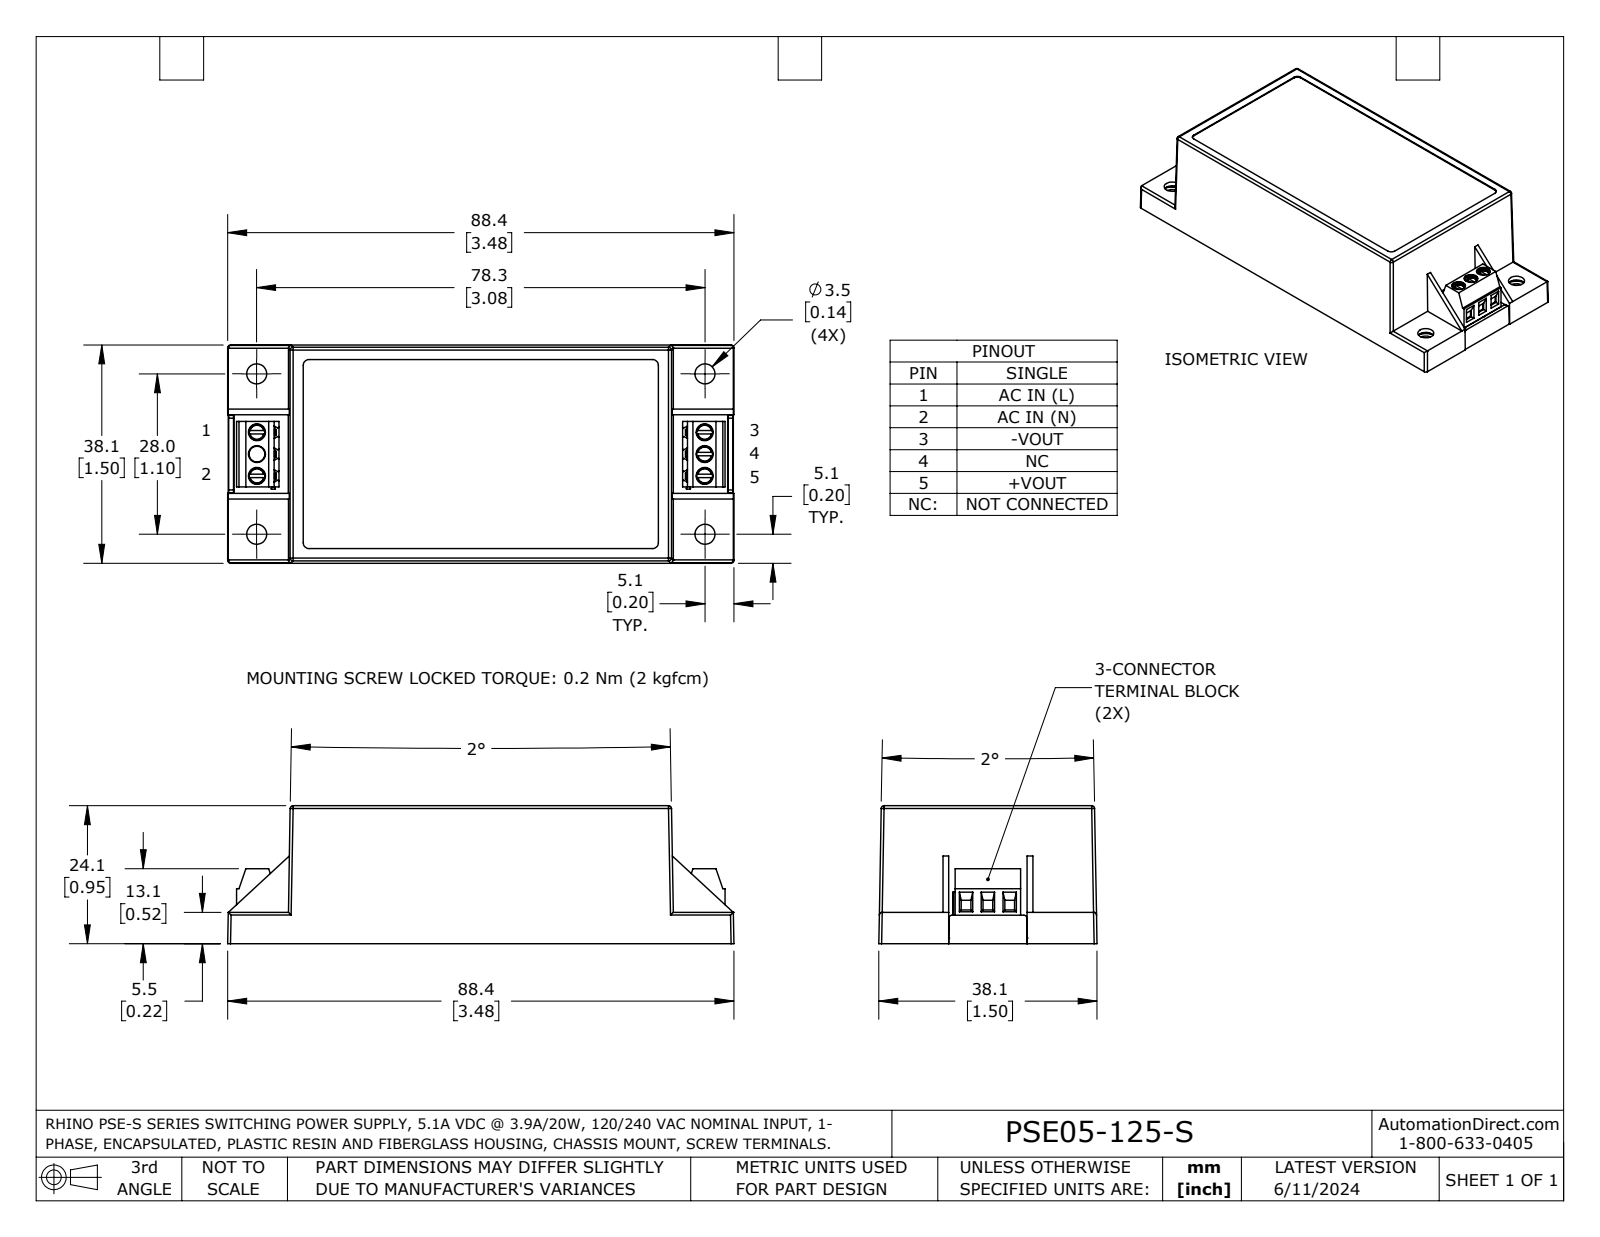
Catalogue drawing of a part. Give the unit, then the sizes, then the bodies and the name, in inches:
Units: inches
Overall size (bounding box): 3.48 × 1.5 × 0.984
Round holes (diameter × count): ⌀0.116 ×6, ⌀0.138 ×4, ⌀0.108 ×1
Partial cylindrical surfaces — rounded edges, fillets, slot ends (radius × count): R0.02 ×19, R0.009 ×18, R0.006 ×12, R0.004 ×8, R0.008 ×4, R0.01 ×4, R0.039 ×4, R0.079 ×4
Main face-to-face distances: 0.039, 0.902, 0.862, 0.941, 1.421, 2.575, 0.177, 0.724, 0.909, 0.176
Hole centre spacings: 0.15, 0.401, 0.551, 0.701, 3.082, 3.079, 0.3, 1.102
Volume: 0.71 in³ · Surface area: 38.5 in²
Bodies: 4 solids, 493 faces (334 planar, 125 cylindrical, 34 other)
Part name (STEP PRODUCT): PSE05-125-S
STEP written by: SolidWorks 2023 (AUTOMOTIVE_DESIGN)
